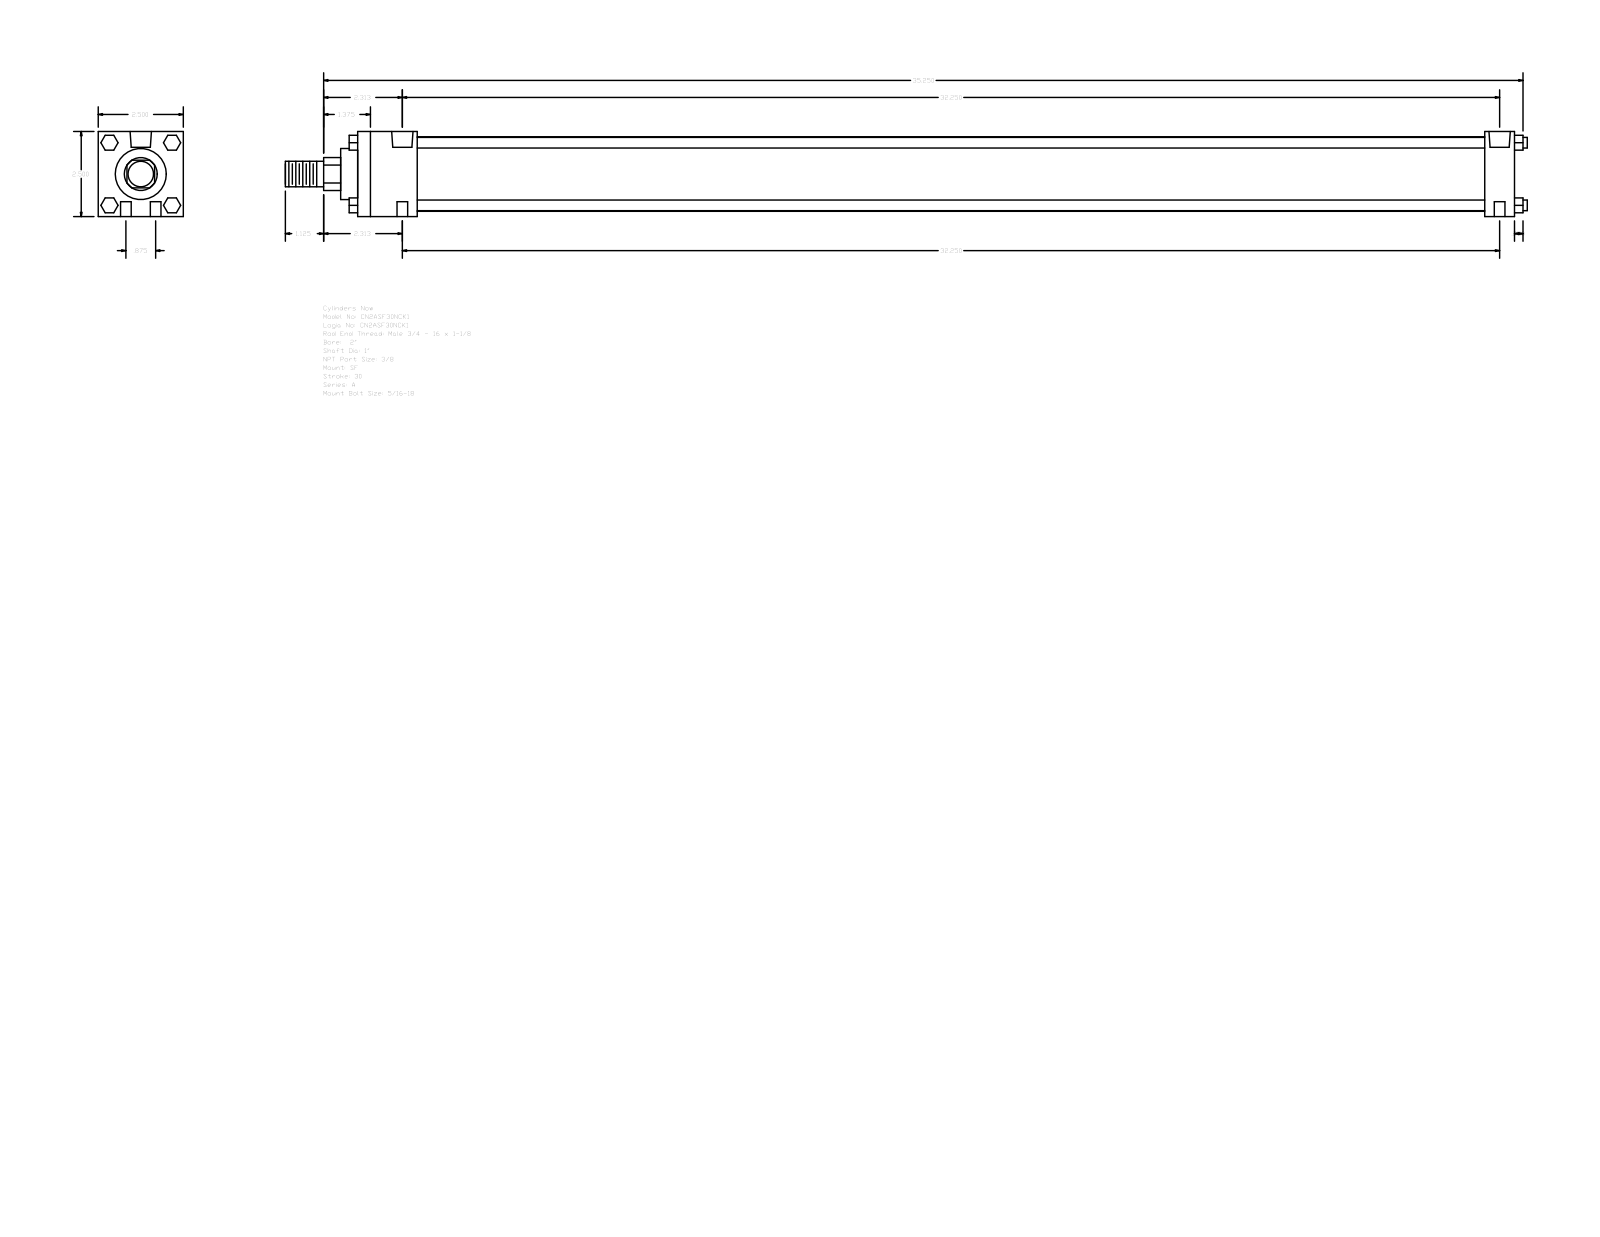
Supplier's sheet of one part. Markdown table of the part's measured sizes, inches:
| quantity | value |
| --- | --- |
| part name | A_SF__0200_1 |
| STEP written by | GSSL Pune (CONFIG_CONTROL_DESIGN) |
| units | inches |
| bodies | 0 solids, 124 faces (94 planar, 30 cylindrical, 0 other) |
| overall size | 36.5 × 2.5 × 2.5 |
| round holes (diameter × count) | 0.313 × 4, 0.219 × 2, 0.627 × 2 |
| round bosses / shafts (diameter × count) | 0.313 × 4, 2.19 × 1, 1.5 × 1, 1 × 1, 0.75 × 1 |
| partial cylindrical surfaces (radius × count) | 0.484 × 1 |
| main face-to-face distances | 2.5, 34, 33.125, 0.875, 1.75, 31.375, 32.25, 0.5, 34.5, 0.25 |
| hole center spacings | 0.437, 32.253, 32.25, 0.875, 32.262, 32.031 |
